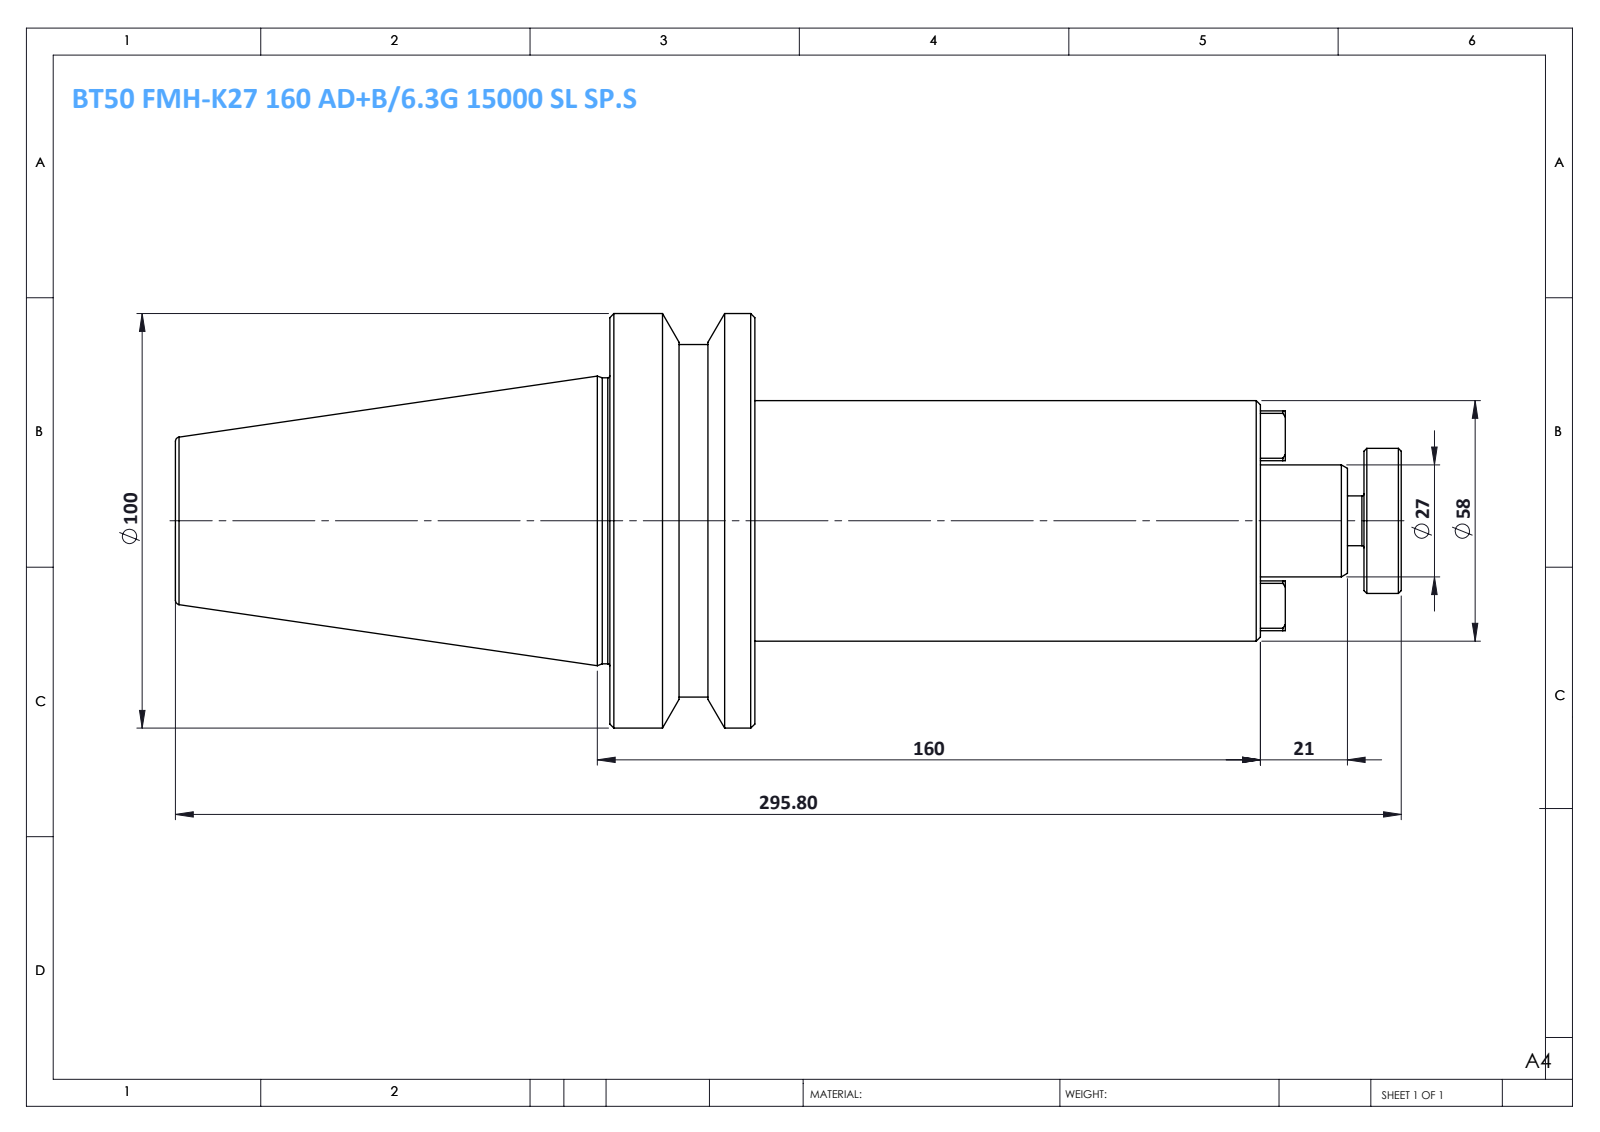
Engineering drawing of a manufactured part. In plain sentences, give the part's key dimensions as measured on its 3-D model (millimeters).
The part is named "BT50 FMH27 160 AD-6.3G 15000 SL SP.S". Its 3-D file was written by "SolidWorks 2014 (CONFIG_CONTROL_DESIGN)". It is 1 solid with 77 faces: 35 planar, 16 cylindrical and 26 other. Overall it measures 295.8 by 100 by 100 millimeters. Its volume is 855 032 cubic millimeters and its surface area 71 504 square millimeters. Round bosses or shafts: 1 of diameter 100, 1 of diameter 85, 1 of diameter 69, 1 of diameter 58, 1 of diameter 35, 1 of diameter 27, 1 of diameter 12. The main face-to-face distances are 35, 122, 157, 261.8, 139.8, 104.8, 34, 156, 191, 295.8.
